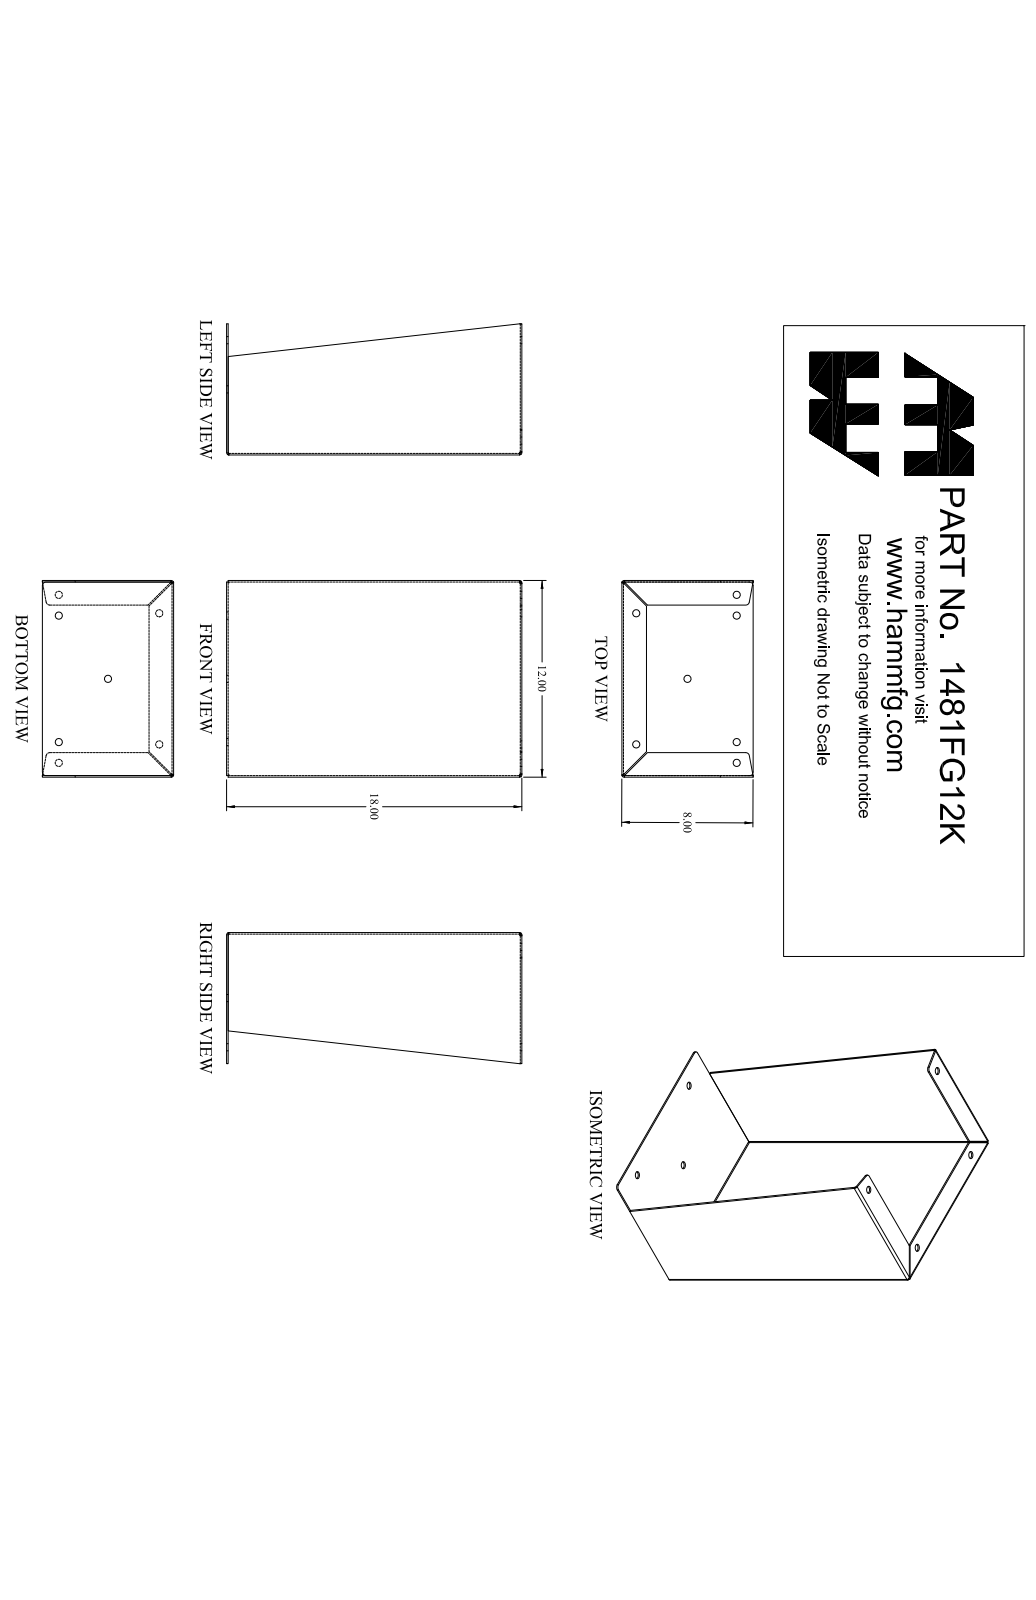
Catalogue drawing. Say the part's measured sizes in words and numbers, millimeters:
The part is named "1481FG12K_Default". Its 3-D file was written by "SolidWorks 2019 (CONFIG_CONTROL_DESIGN)". It is 1 solid with 78 faces: 42 planar, 30 cylindrical and 6 other. Overall it measures 457.2 by 304.8 by 203.2 millimeters. Its volume is 913 600 cubic millimeters and its surface area 764 500 square millimeters. Round holes: 7 of diameter 11.1. Partial cylindrical surfaces (rounded edges, fillets, slot ends): 6 of radius 1.2, 6 of radius 3.6, 4 of radius 5.6. The main face-to-face distances are 2.4, 302.4, 304.8, 300, 2.4, 452.4, 454.8, 454.8, 457.2, 35.7. The hole center spacings are 124.2, 128.9, 155.6, 158.2, 253.1, 32.2, 32.2, 150.9.
